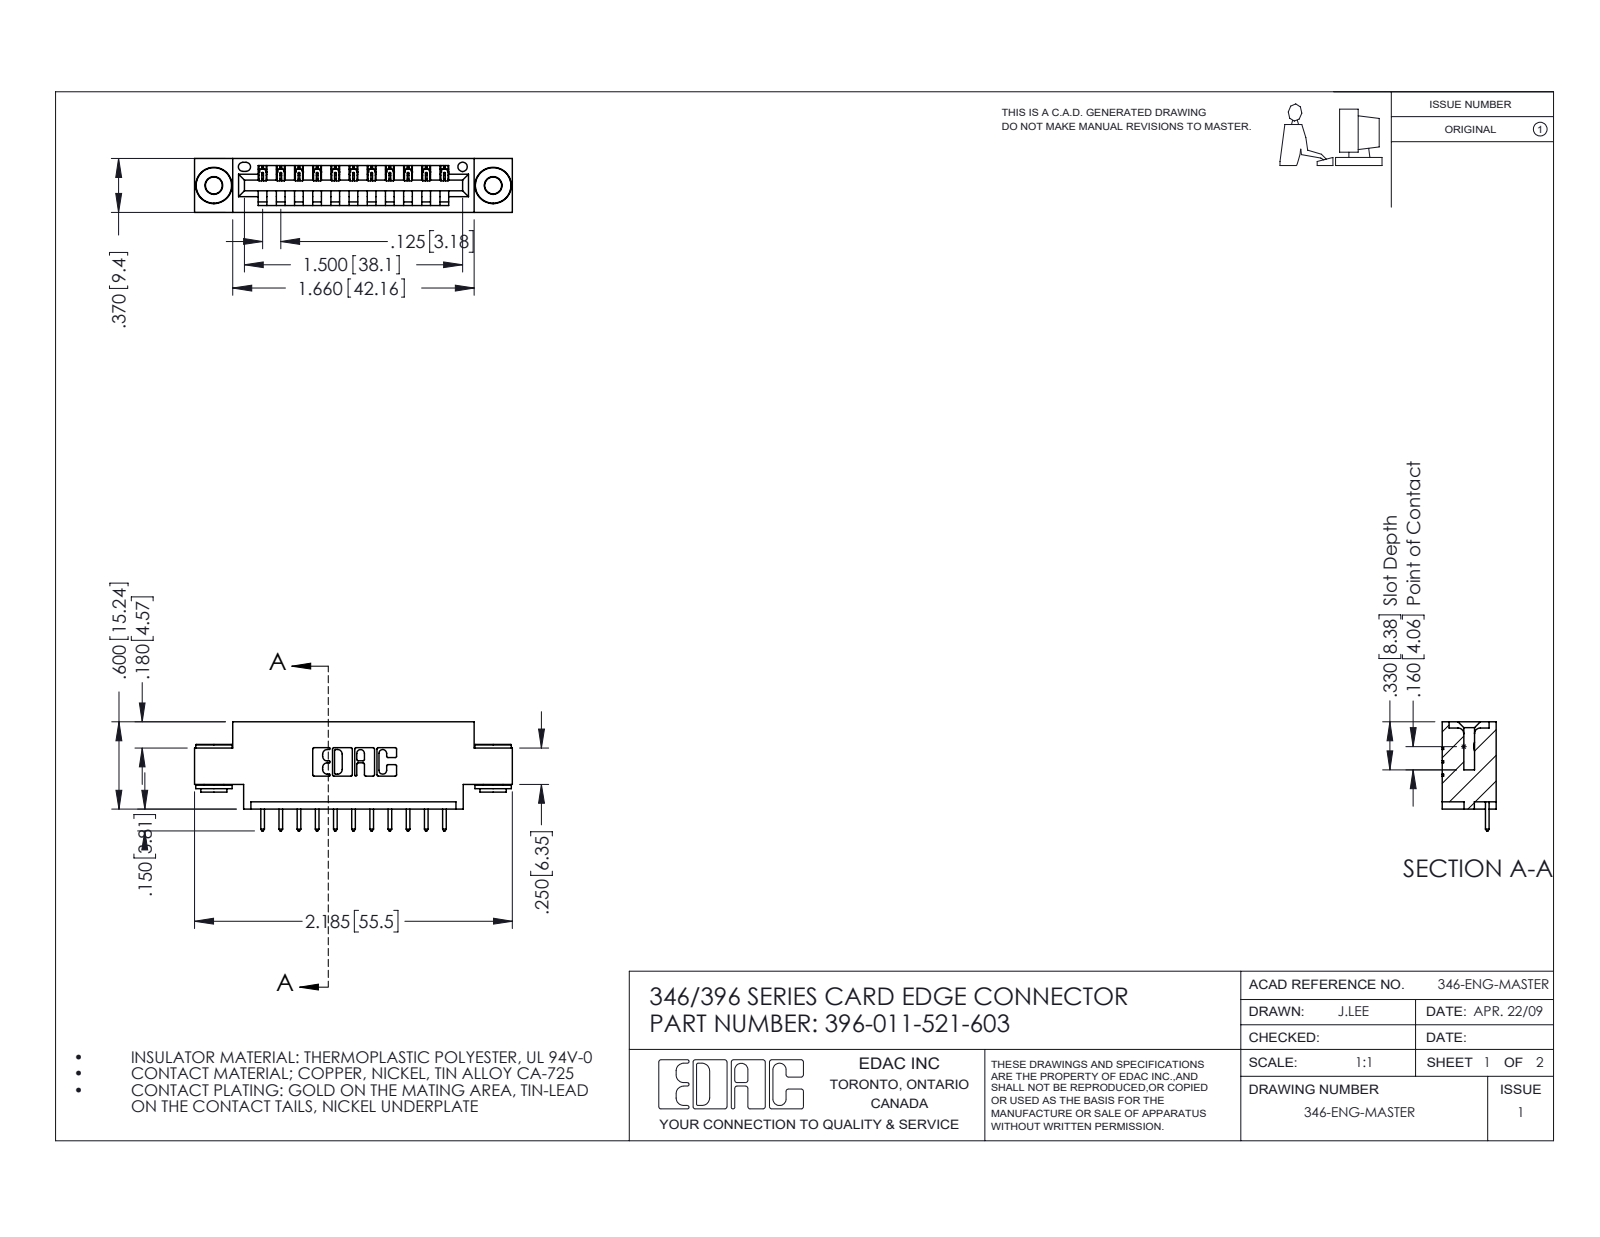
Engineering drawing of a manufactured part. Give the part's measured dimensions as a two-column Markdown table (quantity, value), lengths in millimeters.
| quantity | value |
| --- | --- |
| part name | 345-250-002_345-250-002-102; 396-011-521-603; 346 Part_0.170 Offset - 0.156 Dia-TH; 345-292-001_345-293-121 |
| STEP written by | SolidWorks 2016 (CONFIG_CONTROL_DESIGN) |
| units | millimeters |
| bodies | 14 solids, 802 faces (530 planar, 264 cylindrical, 8 other) |
| overall size | 55.5 × 19.1 × 9.4 |
| volume | 4 930 mm³ |
| surface area | 6 085 mm² |
| round holes (diameter × count) | 2.9 × 2, 4 × 2, 1.6 × 1 |
| round bosses / shafts (diameter × count) | 6.4 × 2, 4.6 × 2, 3.5 × 2 |
| partial cylindrical surfaces (radius × count) | 0.2 × 22, 0.3 × 22, 0.3 × 22, 0.2 × 6, 0.8 × 6, 0.7 × 3, 0.8 × 2, 1 × 2 |
| main face-to-face distances | 6.4, 9.4, 1.2, 8.2, 0.6, 3.8, 5.6, 2.5, 4.4, 1.8 |
| hole center spacings | 6.2, 43.6, 48.8 |
